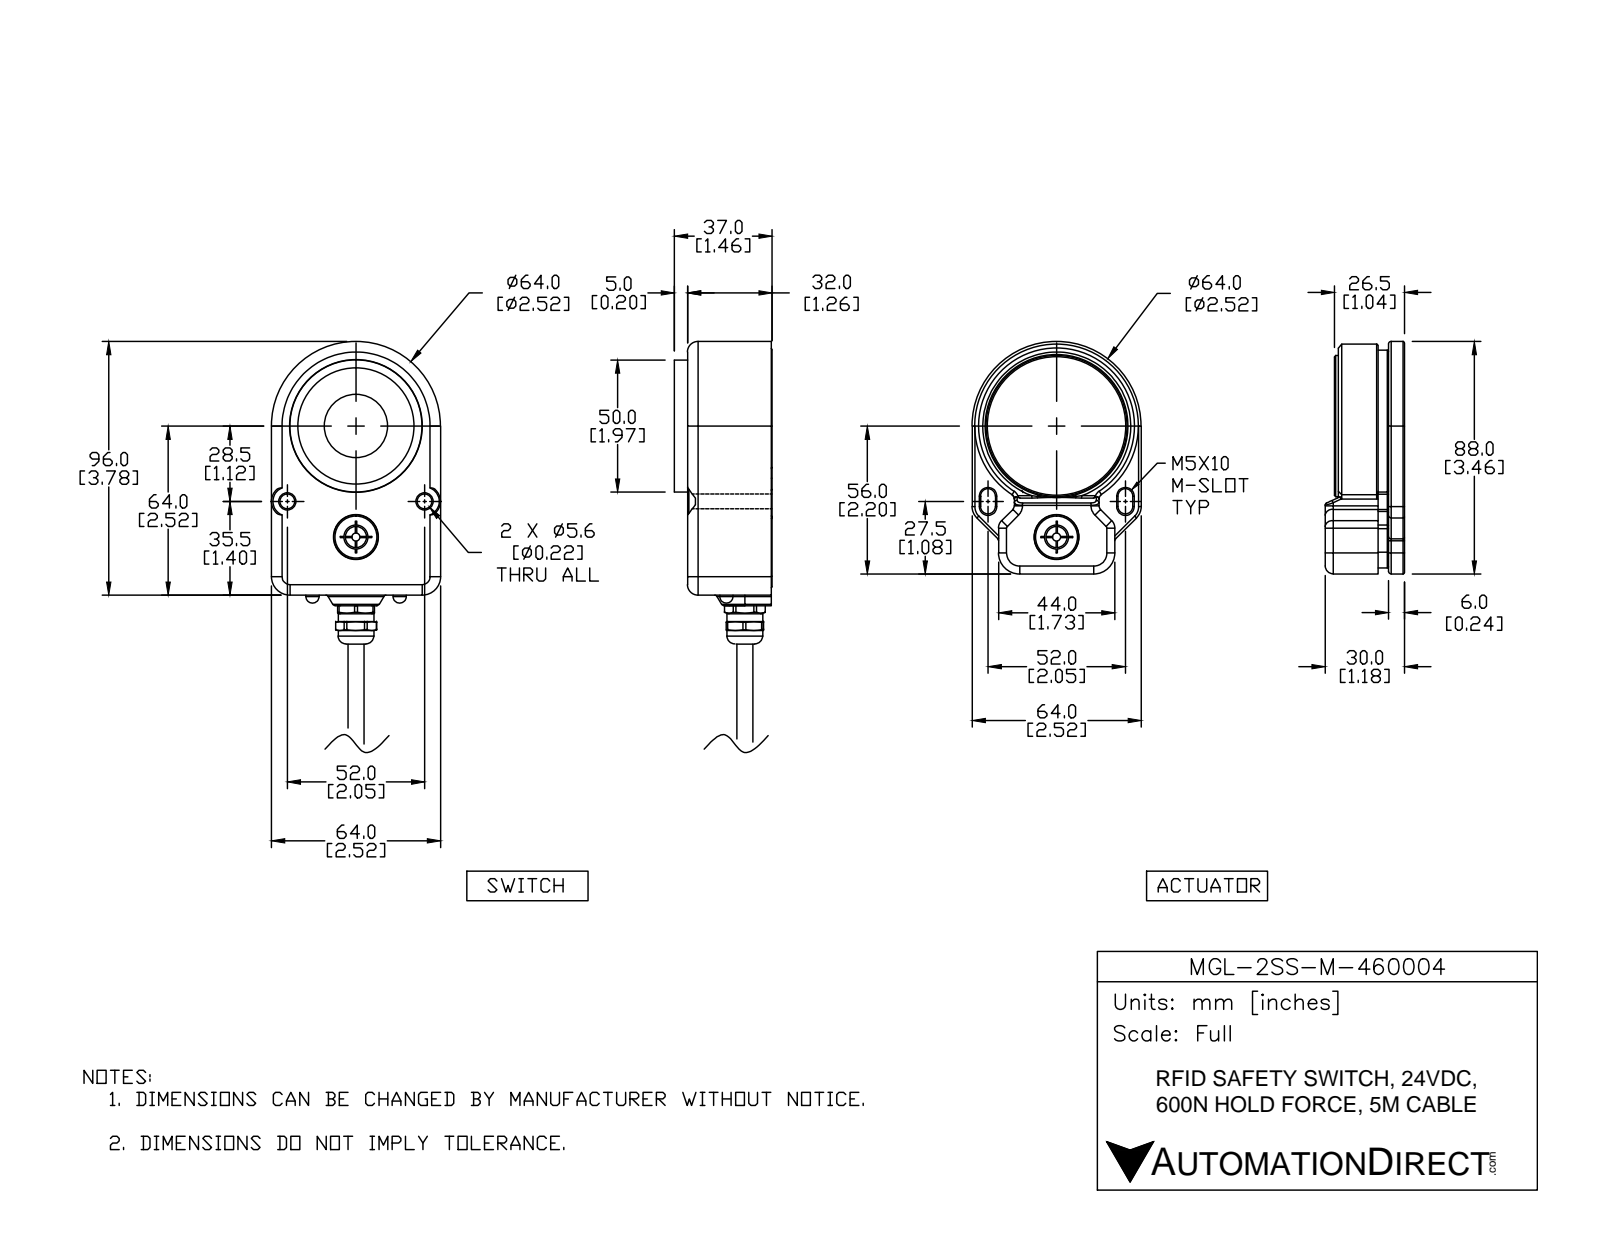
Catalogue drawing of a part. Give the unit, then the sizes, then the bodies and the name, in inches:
Units: inches
Overall size (bounding box): 7.717 × 2.539 × 2.52
Round holes (diameter × count): ⌀0.098 ×8, ⌀0.157 ×8, ⌀0.13 ×6, ⌀0.315 ×6, ⌀0.197 ×5, ⌀0.354 ×3, ⌀0.22 ×2, ⌀0.413 ×2, ⌀0.669 ×2, ⌀0.252 ×1, ⌀0.264 ×1, ⌀0.268 ×1
Round bosses / shafts (diameter × count): ⌀0.02 ×4, ⌀0.236 ×2, ⌀0.228 ×2, ⌀0.22 ×2, ⌀0.118 ×2, ⌀2.441 ×1, ⌀2.26 ×1, ⌀2.102 ×1
Partial cylindrical surfaces — rounded edges, fillets, slot ends (radius × count): R0.02 ×218, R0.039 ×69, R0.079 ×30, R0.012 ×17, R0.118 ×15, R0.157 ×12, R0.236 ×8, R0.024 ×7
Main face-to-face distances: 0.098, 0.236, 0.413, 0.118, 1.89, 0.748, 1.043, 0.394, 1.142, 0.079
Hole centre spacings: 0.706, 0.768, 1.086, 1.024, 2.147, 0.346, 0.376, 0.382
Volume: 12.53 in³ · Surface area: 169.9 in²
Bodies: 20 solids, 1740 faces (445 planar, 724 cylindrical, 571 other)
Part name (STEP PRODUCT): MGL-2SS-M-460004; MGL-2SS-M-460004_2; MGL-2SS-M-460004_1
STEP written by: SolidWorks 2017 (AUTOMOTIVE_DESIGN)
